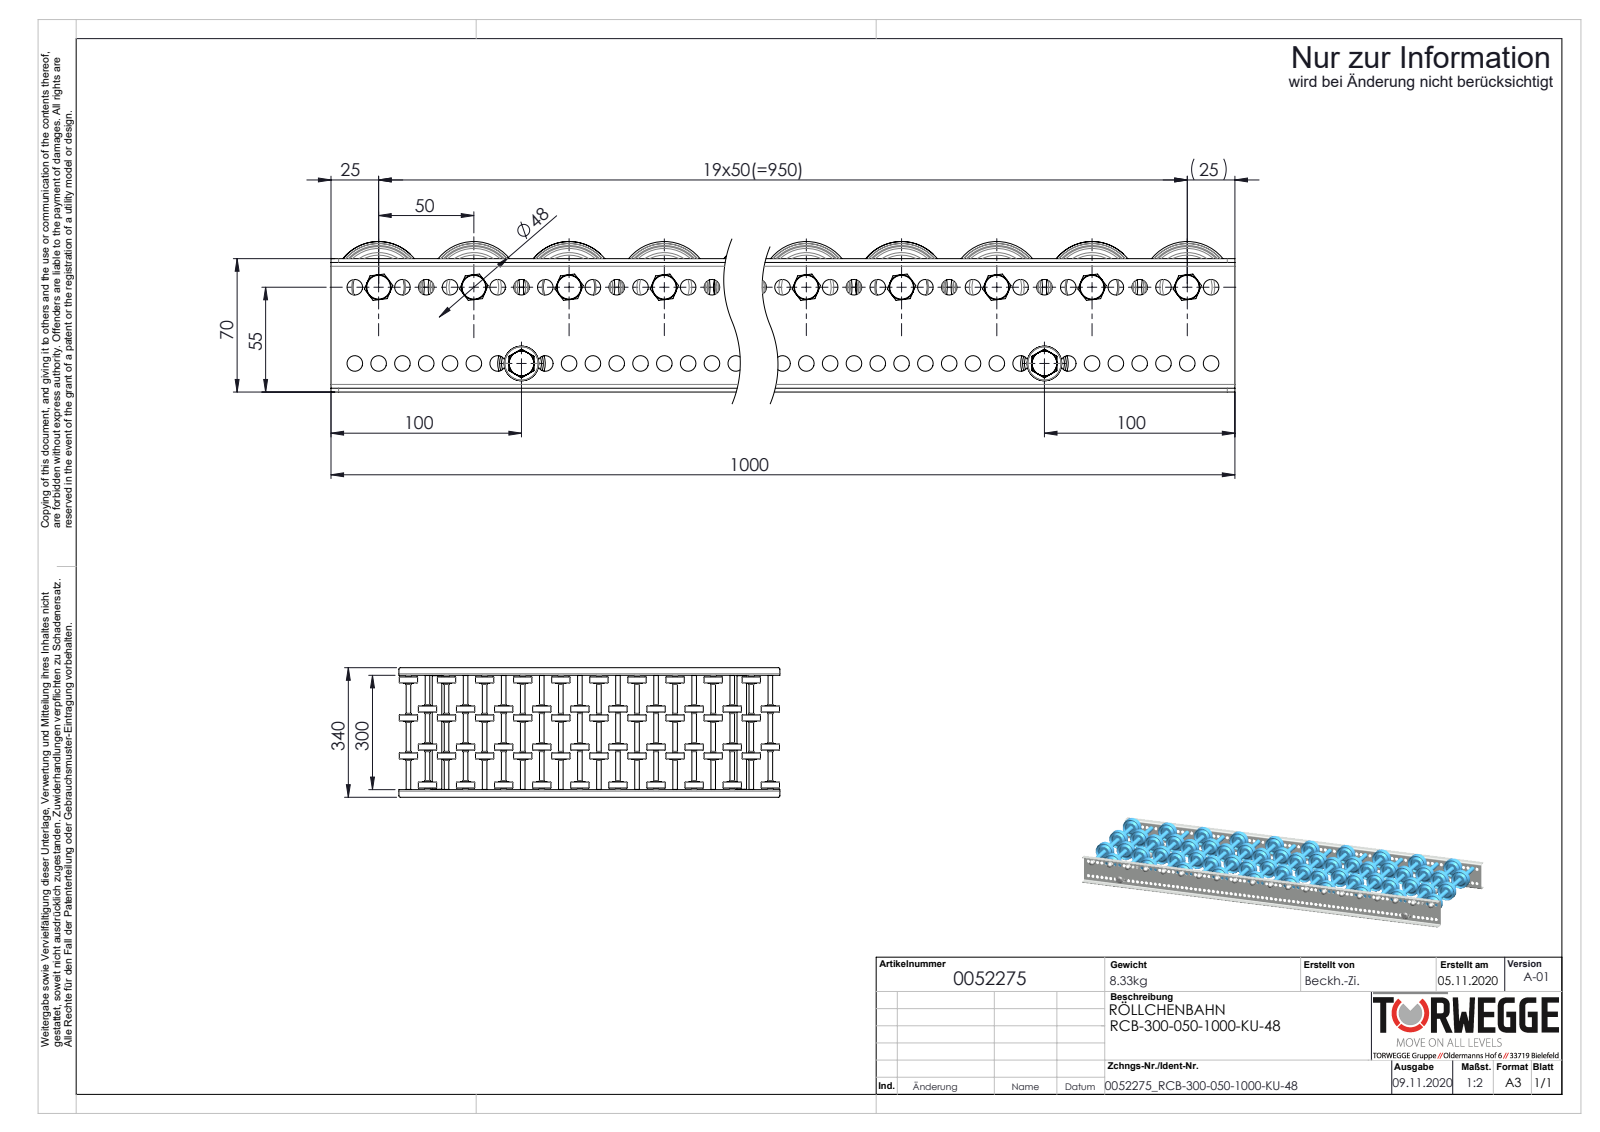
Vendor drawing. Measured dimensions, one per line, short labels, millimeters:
name: 0011532_2300-48-8; Traversen_KFG_L300; 0046278_KB-ROHR-12X1,75mm_KFG_L76; Röllchenachse-für-Konfiguration_EL300 (+5 more)
written by: SolidWorks 2020 (AUTOMOTIVE_DESIGN)
unit: mm
bodies: 192 solids, 6692 faces (1260 planar, 2208 cylindrical, 3224 other)
size: 1000 × 340 × 79
volume: 2 185 000 mm³; area: 1 595 000 mm²
holes: 158× ⌀8.2, 20× ⌀6.65, 20× ⌀9.65, 20× ⌀13.7, 2× ⌀6.8, 2× ⌀21
bosses: 22× ⌀8, 20× ⌀48, 20× ⌀27, 20× ⌀12.7, 20× ⌀12.5, 20× ⌀12, 2× ⌀25
rounds: 8× R4, 4× R2
face distances: 2, 302, 68, 304, 300, 99.8, 66, 70, 16.3, 76.1
hole spacings: 12.5, 25, 37.5, 50, 62.5, 75, 87.5, 100
